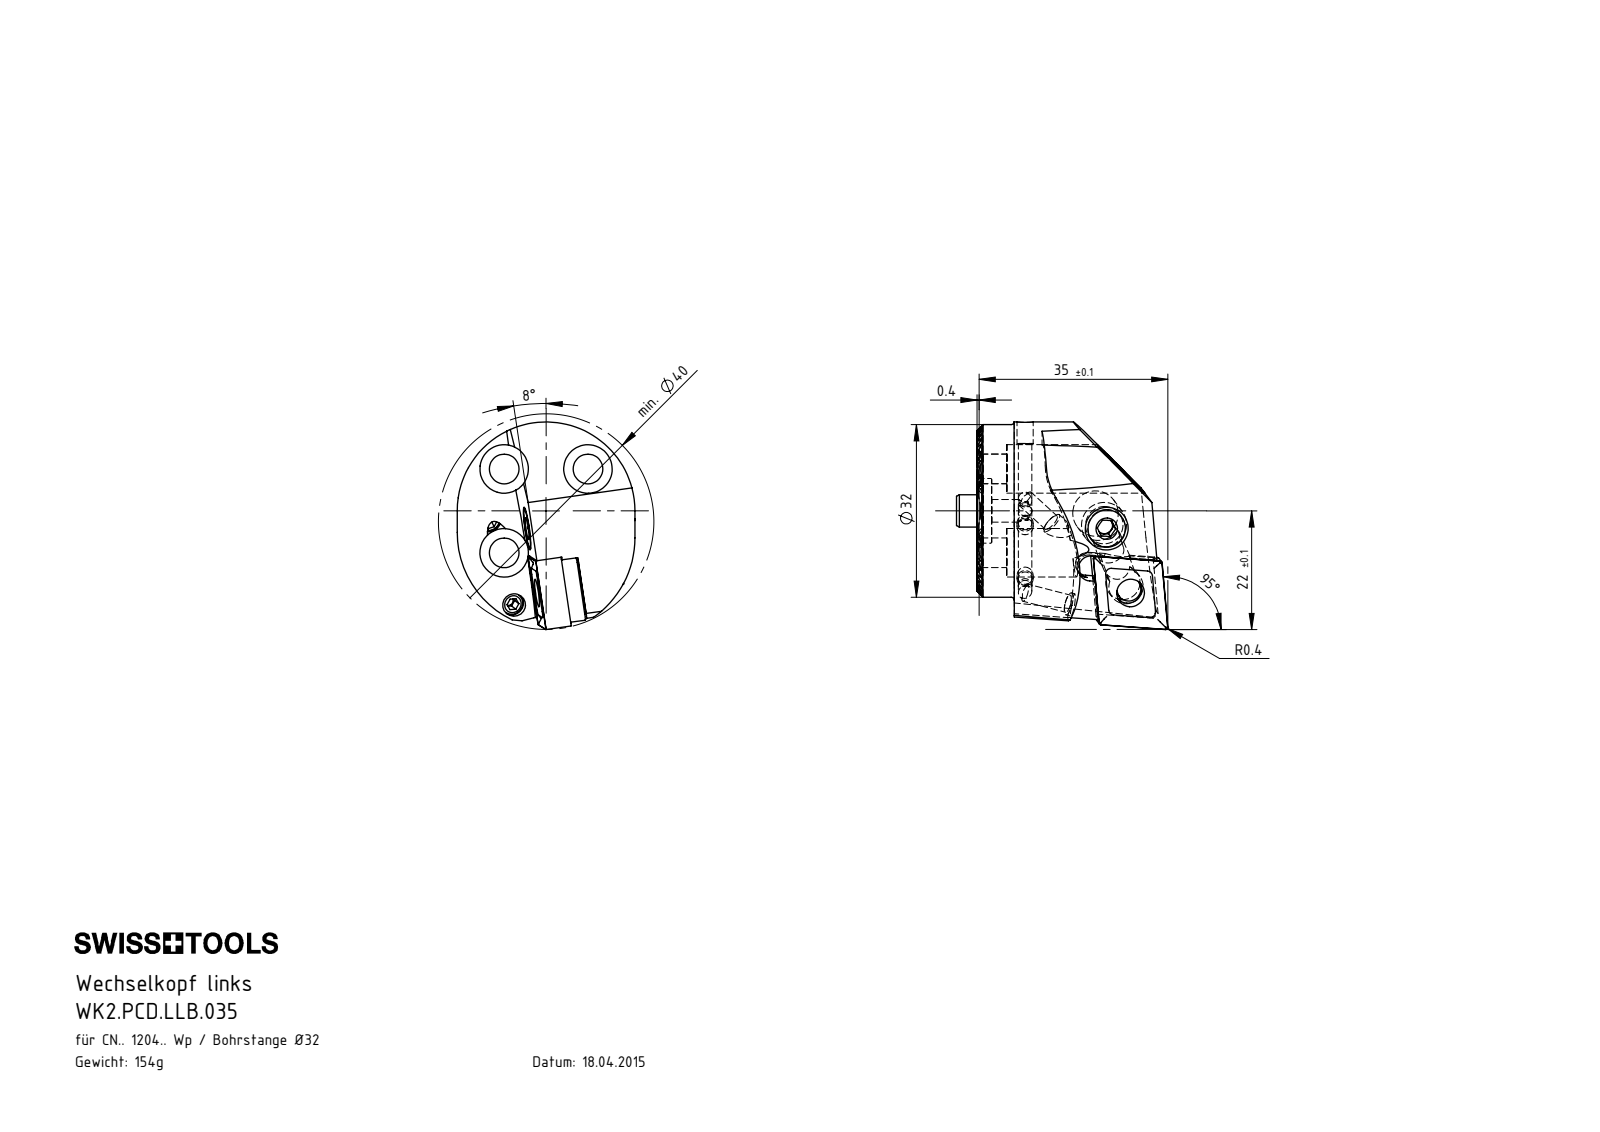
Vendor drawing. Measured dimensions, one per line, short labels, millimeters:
name: CNMG120404; WK2.PCD.LLB.035; WCD-ER2.101.003_A; KVT_MB_600_030 (+5 more)
written by: SolidWorks 2017 (AUTOMOTIVE_DESIGN)
unit: mm
bodies: 14 solids, 626 faces (234 planar, 204 cylindrical, 188 other)
size: 39.21 × 38.51 × 33.06
volume: 18 745 mm³; area: 10 918 mm²
holes: 3× ⌀2.38, 3× ⌀2.5, 3× ⌀4.2, 3× ⌀5.5, 3× ⌀9, 2× ⌀1.7, 2× ⌀3.3, 1× ⌀3, 1× ⌀5.16, 1× ⌀6.4, 1× ⌀7, 1× ⌀8.4
bosses: 3× ⌀3, 2× ⌀4, 1× ⌀32, 1× ⌀8, 1× ⌀7.9, 1× ⌀6.4, 1× ⌀6, 1× ⌀4.5
rounds: 22× R0.12, 4× R0.4, 4× R1, 2× R2.5, 2× R18, 1× R2.1, 1× R2.2, 1× R2.35
face distances: 1.3, 2.6, 3.9, 5.2, 6.5, 12.99, 11.69, 14.29, 7.8, 10.39
hole spacings: 11, 15.56, 12.8, 12.85, 22.01
